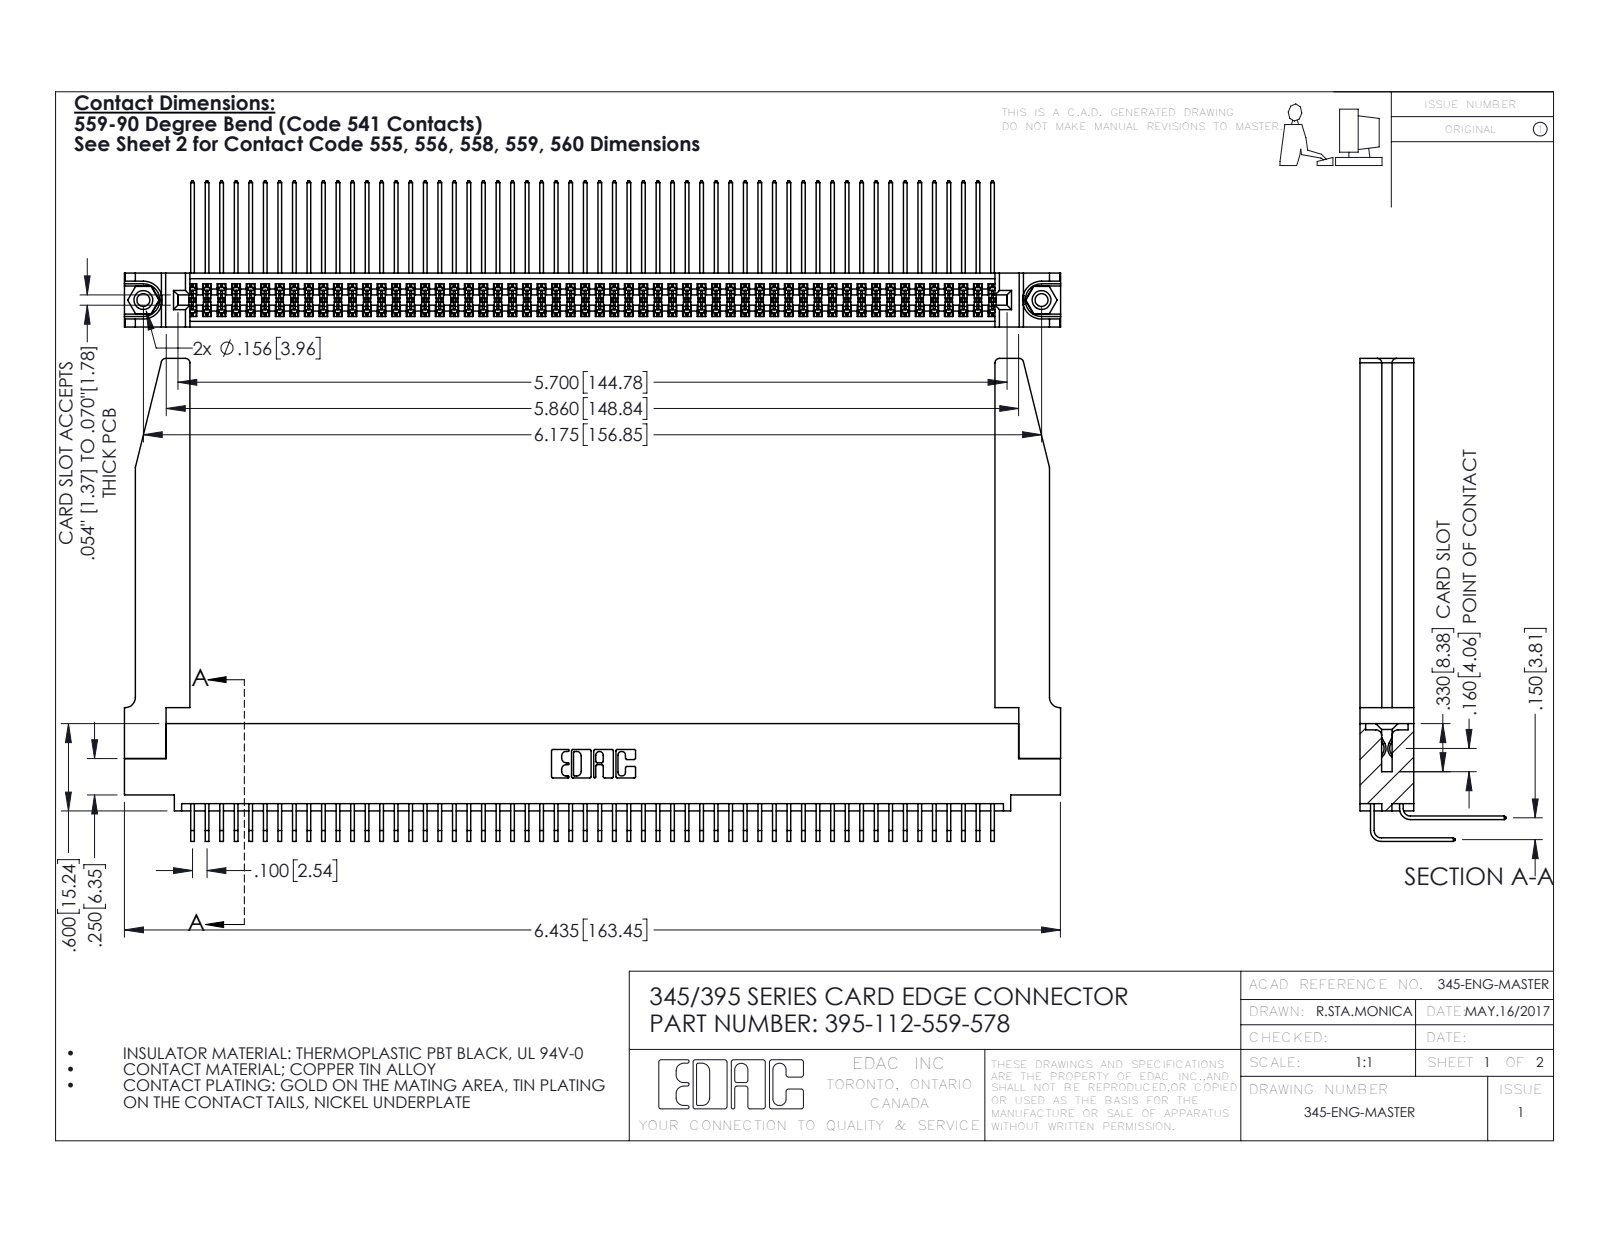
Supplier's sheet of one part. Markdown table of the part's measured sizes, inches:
| quantity | value |
| --- | --- |
| part name | 345-250-001_345-250-001-102; 395-112-559-578; 345-220-078_345-220-078; 345-292-001_559 Tail - 2 (+2 more) |
| STEP written by | SolidWorks 2016 (CONFIG_CONTROL_DESIGN) |
| units | inches |
| bodies | 117 solids, 6188 faces (4146 planar, 1990 cylindrical, 52 other) |
| overall size | 6.436 × 3.319 × 1.005 |
| volume | 1.486 in³ |
| surface area | 53.87 in² |
| round holes (diameter × count) | 0.089 × 2, 0.125 × 2, 0.156 × 2, 0.064 × 1 |
| round bosses / shafts (diameter × count) | 0.155 × 2 |
| partial cylindrical surfaces (radius × count) | 0.006 × 168, 0.01 × 22, 0.03 × 8, 0.007 × 6, 0.031 × 6, 0.026 × 3, 0.014 × 2, 0.019 × 2 |
| main face-to-face distances | 0.072, 0.298, 0.37, 0.2, 0.098, 0.272, 0.025, 0.225, 0.175, 0.15 |
| hole center spacings | 0.27, 5.939, 6.175 |
